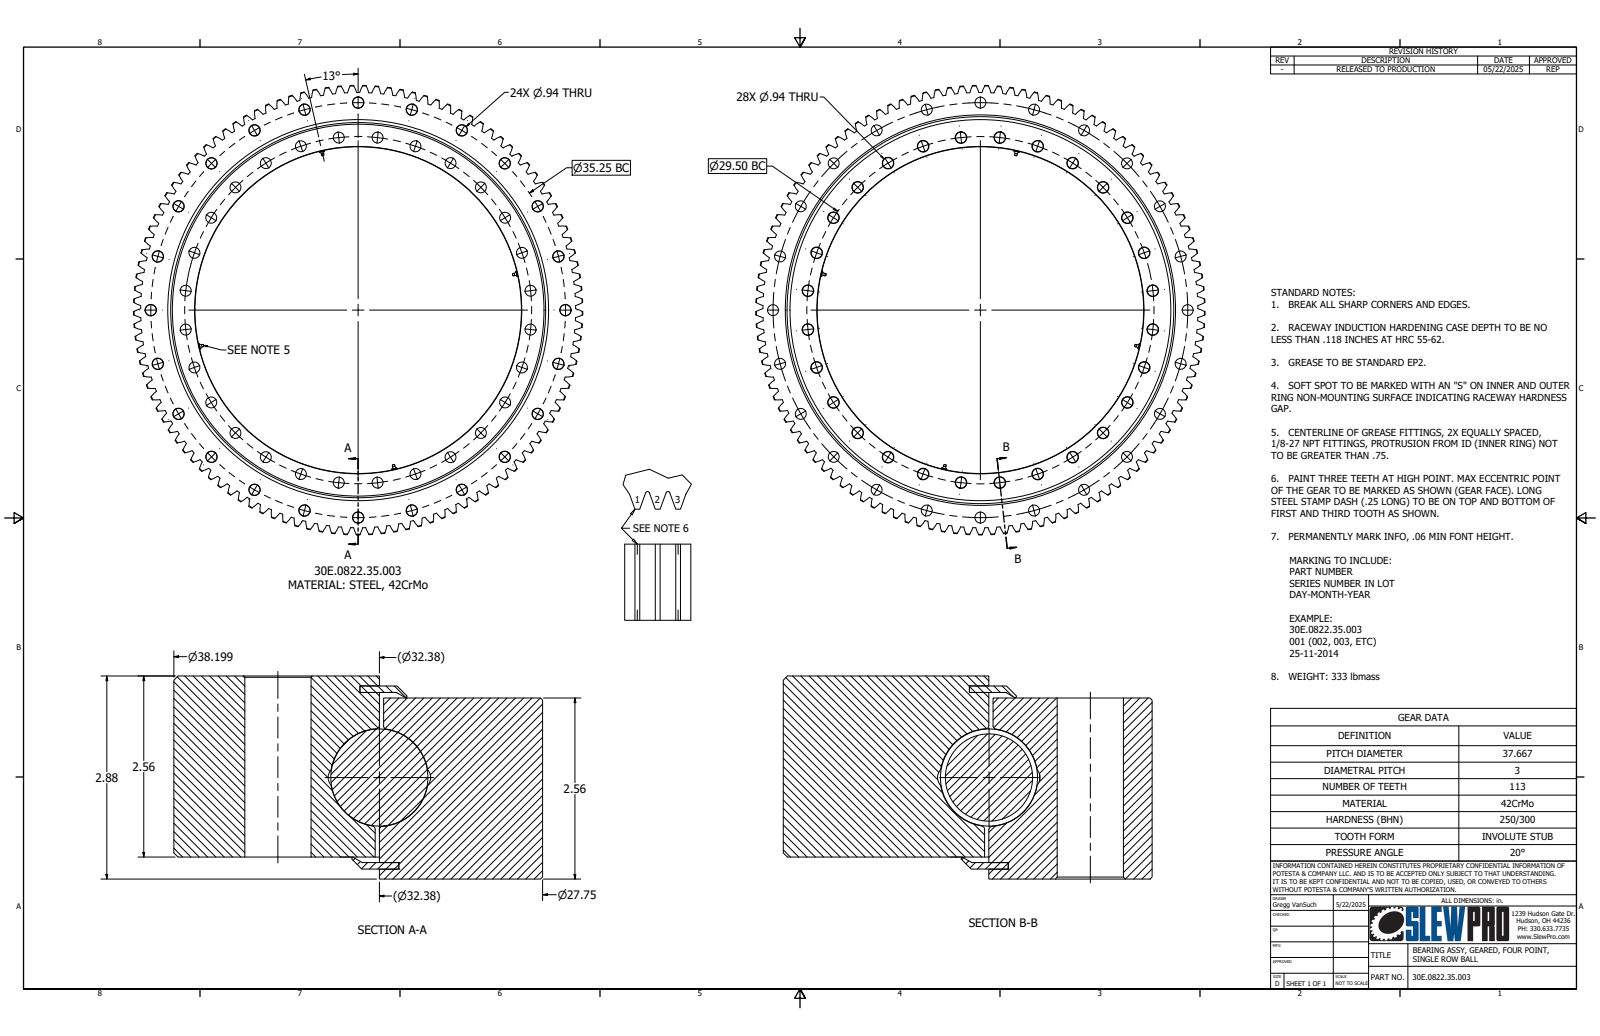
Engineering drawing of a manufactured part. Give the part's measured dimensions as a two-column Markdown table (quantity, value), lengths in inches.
| quantity | value |
| --- | --- |
| part name | 30E.0822.35.003; Spur Gears1; 1_8 NPT Fitting |
| STEP written by | Autodesk Inventor 2026 (AUTOMOTIVE_DESIGN) |
| units | inches |
| bodies | 10 solids, 1059 faces (58 planar, 528 cylindrical, 473 other) |
| overall size | 38.198 × 38.195 × 2.875 |
| volume | 1 173 in³ |
| surface area | 3 588 in² |
| round holes (diameter × count) | 0.938 × 52, 0.1 × 4, 1.502 × 1, 27.75 × 1, 31.825 × 1, 32.495 × 1, 32.926 × 1 |
| round bosses / shafts (diameter × count) | 32.925 × 1, 32.375 × 1, 32.255 × 1, 31.824 × 1, 1.5 × 1 |
| partial cylindrical surfaces (radius × count) | 3.586 × 226, 18.483 × 1, 19.099 × 1 |
| main face-to-face distances | 2.563, 0.312, 2.875, 2.251, 2.501, 0.093, 0.141, 2.734, 0.171, 2.422 |
| hole center spacings | 9.743, 12.8, 3.303, 6.565, 14.75, 20.86, 15.695, 18.393 |
